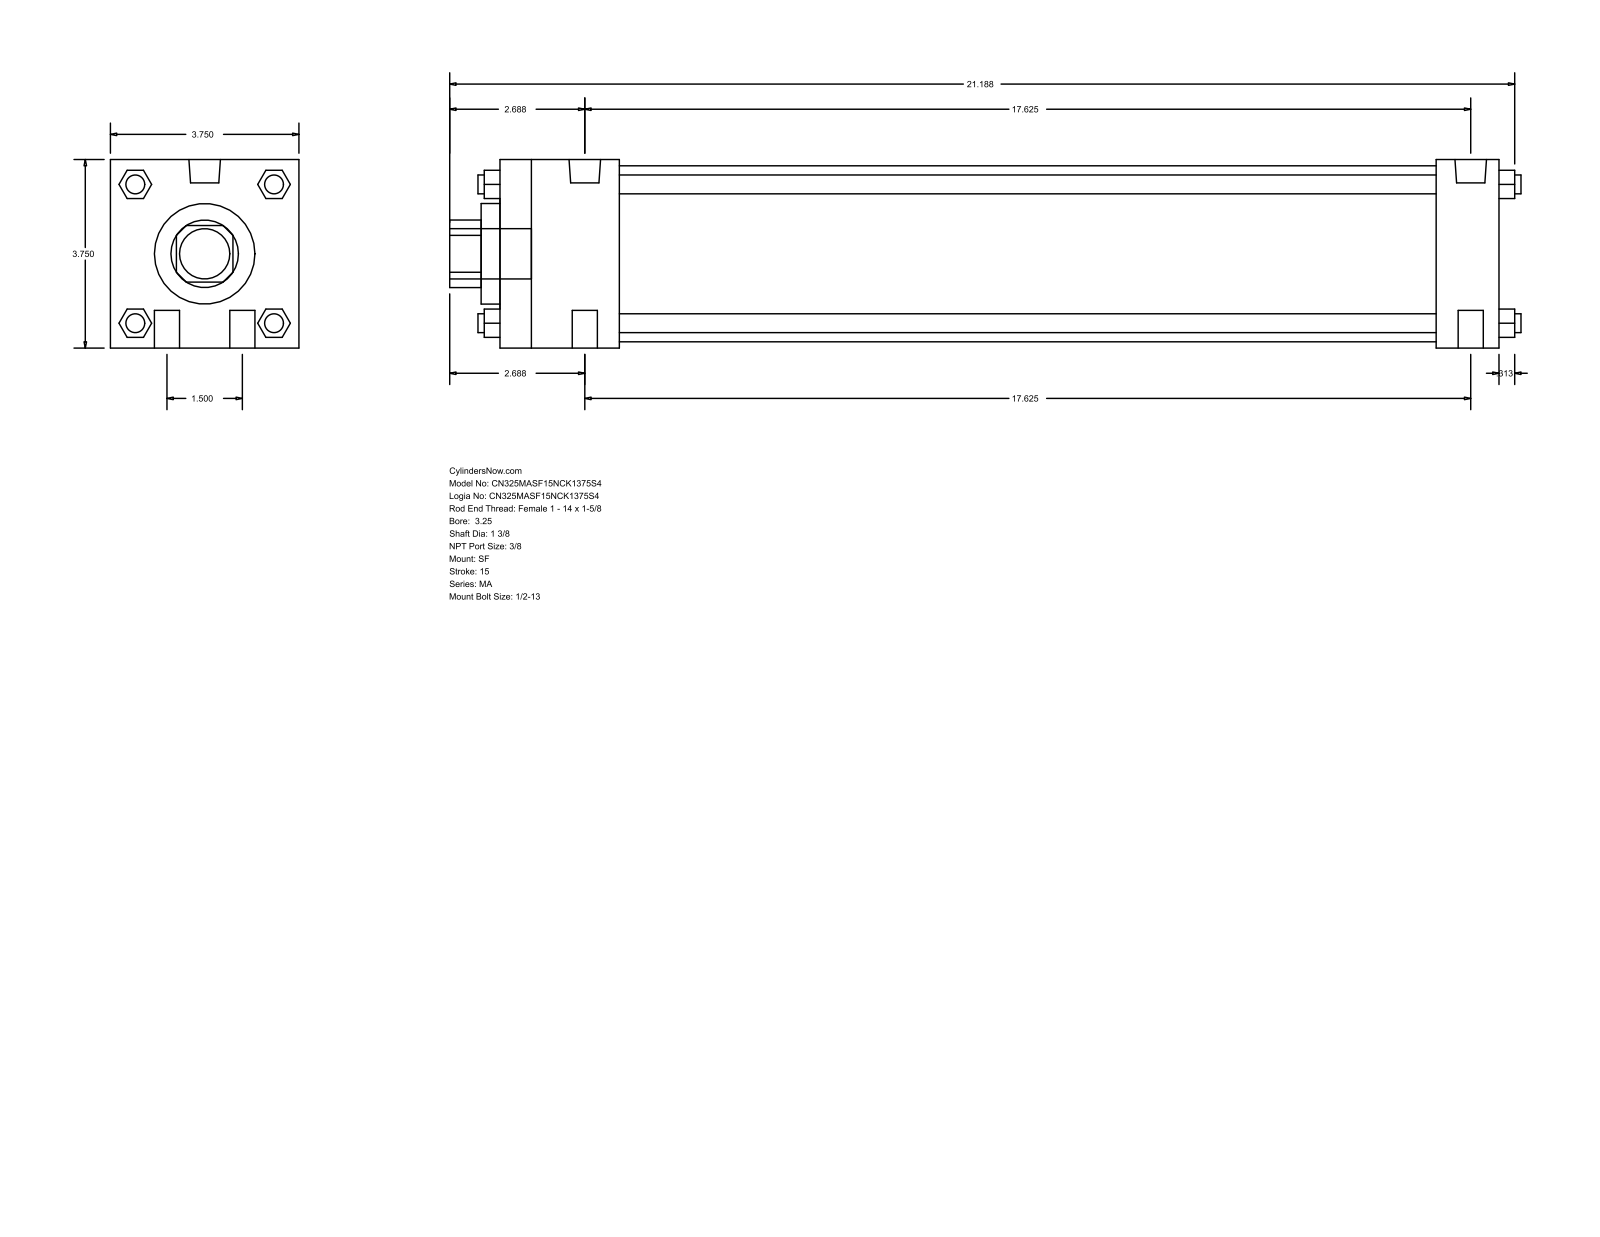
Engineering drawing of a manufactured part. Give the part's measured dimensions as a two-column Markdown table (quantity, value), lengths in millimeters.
| quantity | value |
| --- | --- |
| part name | MA_SF__0325_1.375 |
| STEP written by | GSSL Pune (CONFIG_CONTROL_DESIGN) |
| units | millimeters |
| bodies | 0 solids, 124 faces (94 planar, 30 cylindrical, 0 other) |
| overall size | 541.34 × 95.25 × 95.25 |
| round holes (diameter × count) | 34.92 × 1, 50.8 × 1, 88.9 × 1 |
| round bosses / shafts (diameter × count) | 12.7 × 4, 9.53 × 4, 15.93 × 2, 11.11 × 2, 25.4 × 1 |
| partial cylindrical surfaces (radius × count) | 17.06 × 1 |
| main face-to-face distances | 95.24, 504.83, 473.08, 31.75, 60.32, 412.76, 444.51, 9.52, 69.84, 482.6 |
